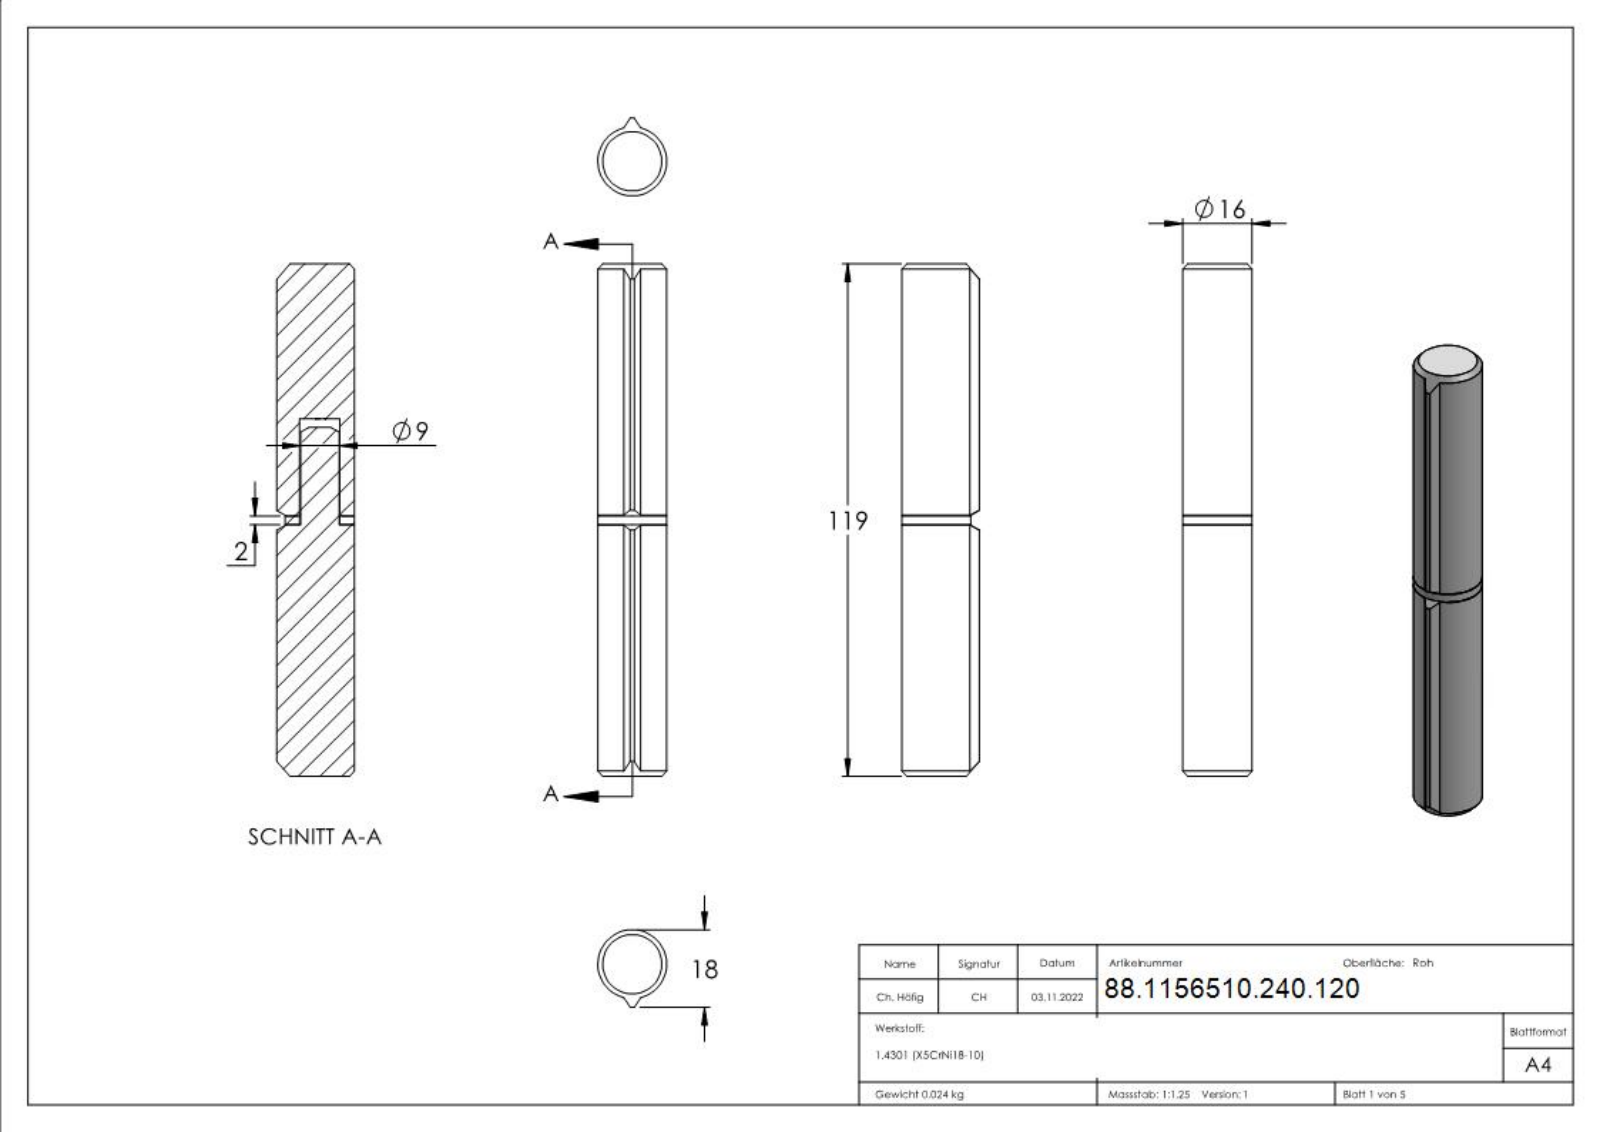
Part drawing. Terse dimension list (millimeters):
name: 56510-240-120; 56510-240 Teil1_56510-240-120 Teil1; 56510-240 Teil2_56510-240-120 Teil2; 56510-240 Teil3_56510-240-120 Teil3
written by: SolidWorks 2018 (CONFIG_CONTROL_DESIGN)
unit: mm
bodies: 3 solids, 324 faces (180 planar, 6 cylindrical, 138 other)
size: 119 × 18 × 16
volume: 24 146 mm³; area: 8 562 mm²
holes: 1× ⌀9.3
bosses: 1× ⌀16, 1× ⌀9
face distances: 58.5, 60.5, 2, 119, 22.5, 83, 24.5, 36, 81, 20.5
